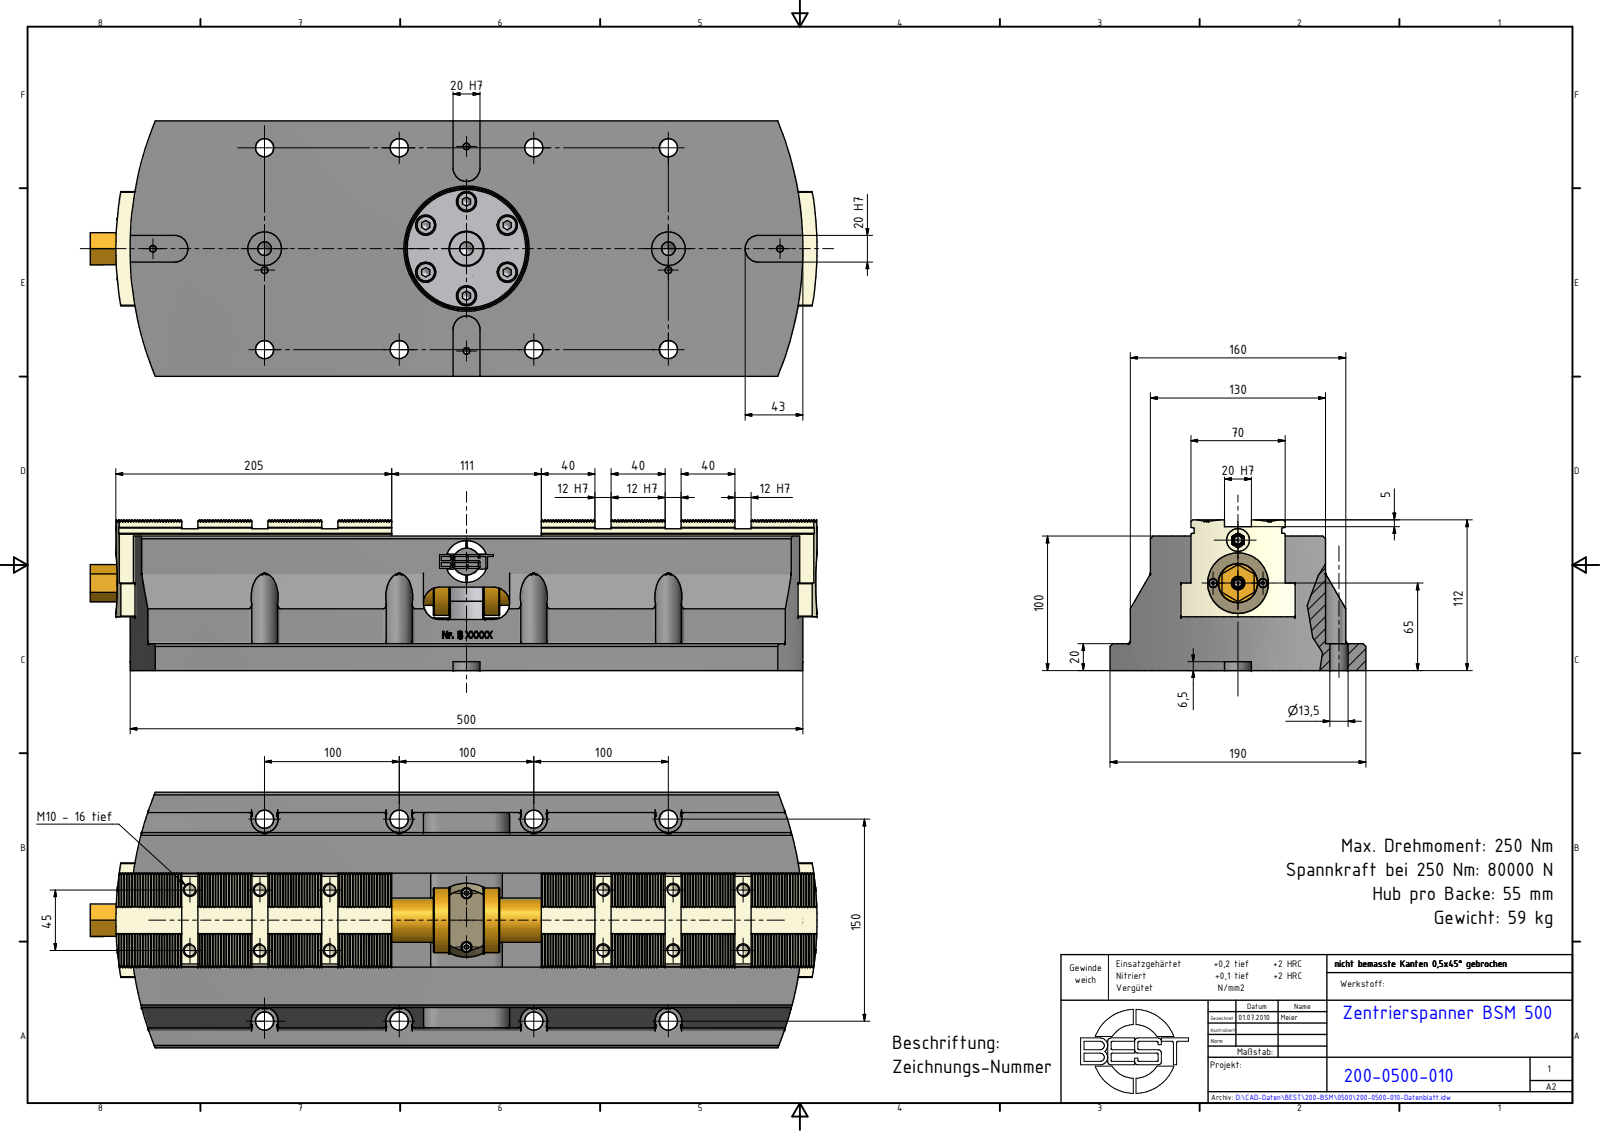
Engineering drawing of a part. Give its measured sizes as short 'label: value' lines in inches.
name: 200-0500-010-Kunde
written by: Autodesk Inventor 2010 (CONFIG_CONTROL_DESIGN)
unit: in
bodies: 3 solids, 757 faces (452 planar, 134 cylindrical, 171 other)
size: 21.22 × 7.48 × 4.409
volume: 446.1 in³; area: 615.9 in²
holes: 1× ⌀0.157, 1× ⌀0.669
bosses: 1× ⌀3.543, 1× ⌀1.89, 1× ⌀1.26, 1× ⌀1.142, 1× ⌀0.272
rounds: 20× R0.02, 20× R0.079, 12× R0.049, 5× R0.394, 4× R0.061, 4× R0.111, 3× R9.843, 2× R0.472
face distances: 3.937, 0.472, 0.591, 4.409, 1.181, 1.772, 0.787, 2.756, 2.362, 0.197
